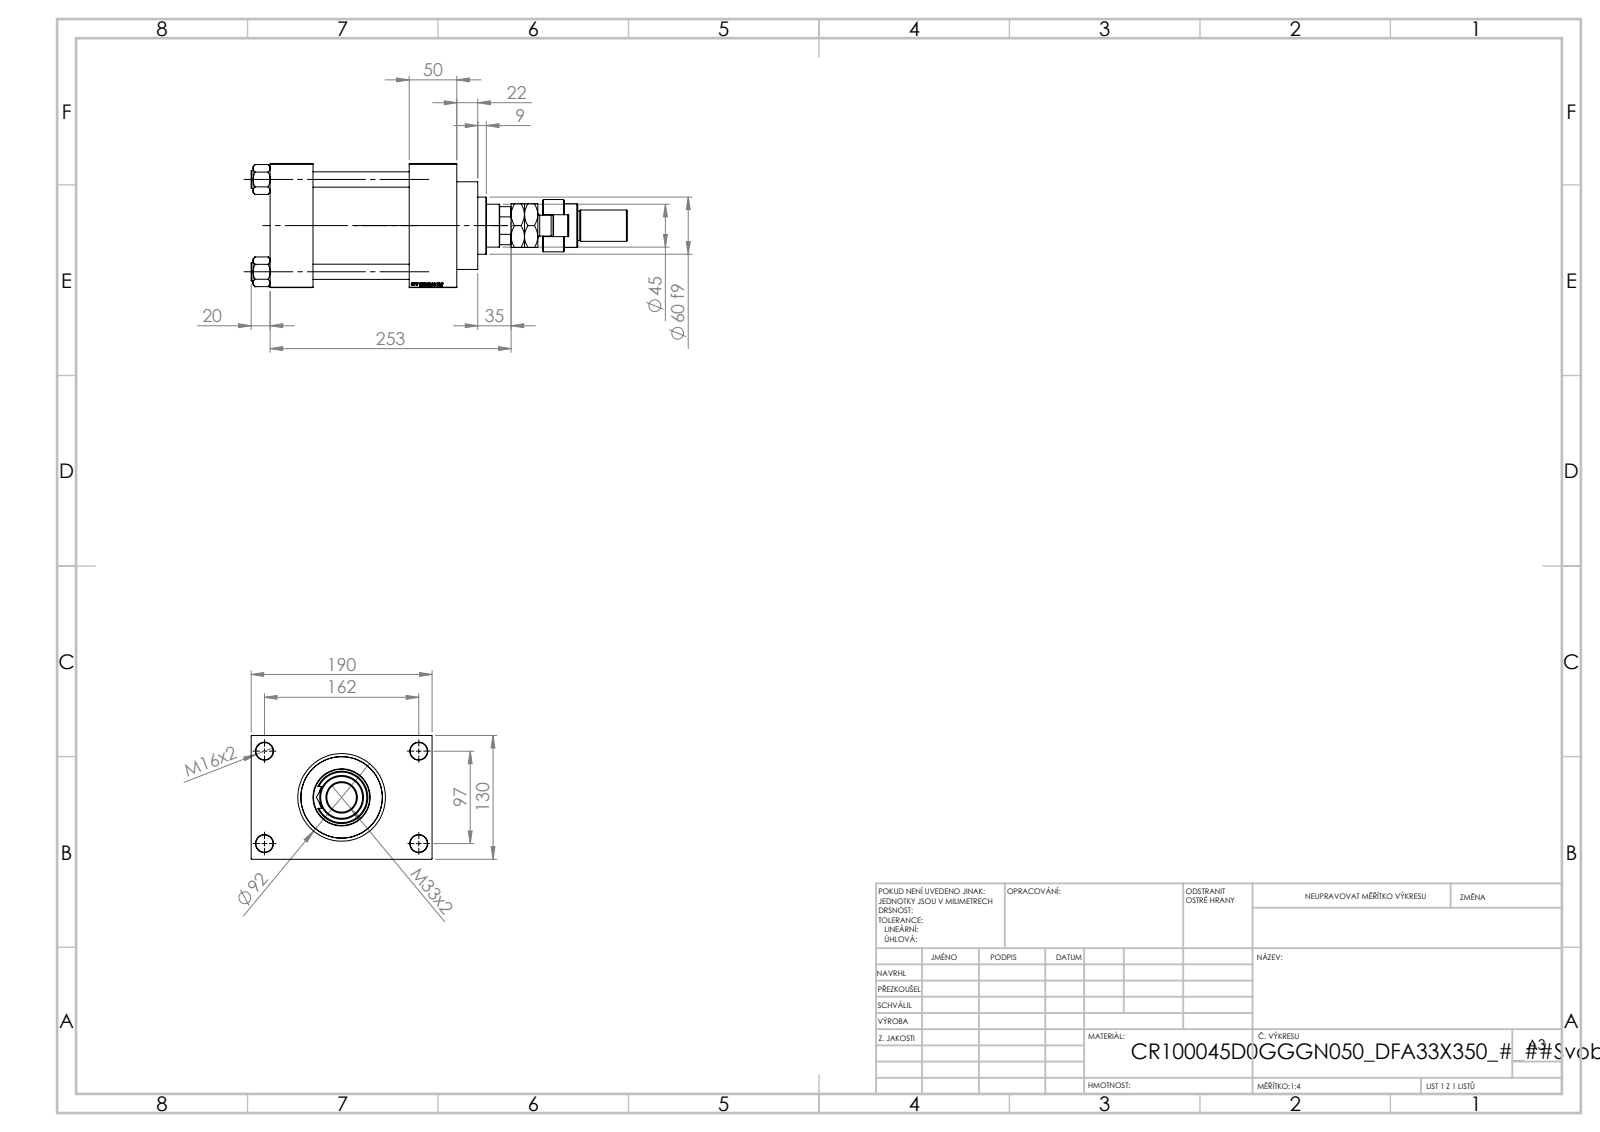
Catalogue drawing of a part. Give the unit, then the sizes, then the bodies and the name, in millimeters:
Units: millimetres
Overall size (bounding box): 395 × 190 × 130
Round holes (diameter × count): ⌀16 ×4, ⌀18 ×4, ⌀7 ×2, ⌀26.44 ×2, ⌀35 ×2, ⌀31.5 ×1, ⌀39 ×1, ⌀45 ×1, ⌀48 ×1, ⌀76 ×1, ⌀85.5 ×1, ⌀100 ×1
Round bosses / shafts (diameter × count): ⌀19 ×4, ⌀106 ×1, ⌀92 ×1, ⌀60 ×1, ⌀55 ×1, ⌀46 ×1, ⌀35 ×1, ⌀33 ×1
Partial cylindrical surfaces — rounded edges, fillets, slot ends (radius × count): R11.5 ×1, R22 ×1
Main face-to-face distances: 50, 130, 45, 101, 151, 146, 196, 30, 160, 190
Hole centre spacings: 32.55, 68.52, 94.41, 96.9, 102.27, 129.45, 161.73, 97
Volume: 2 870 000 mm³ · Surface area: 412 839 mm²
Bodies: 13 solids, 1237 faces (573 planar, 102 cylindrical, 562 other)
Part name (STEP PRODUCT): V215CR_D_TYCINKA; MFA; FEMALE_PART_FOR_DFA; V215CR_D_Body (+3 more)
STEP written by: SolidWorks 2019 (CONFIG_CONTROL_DESIGN)
